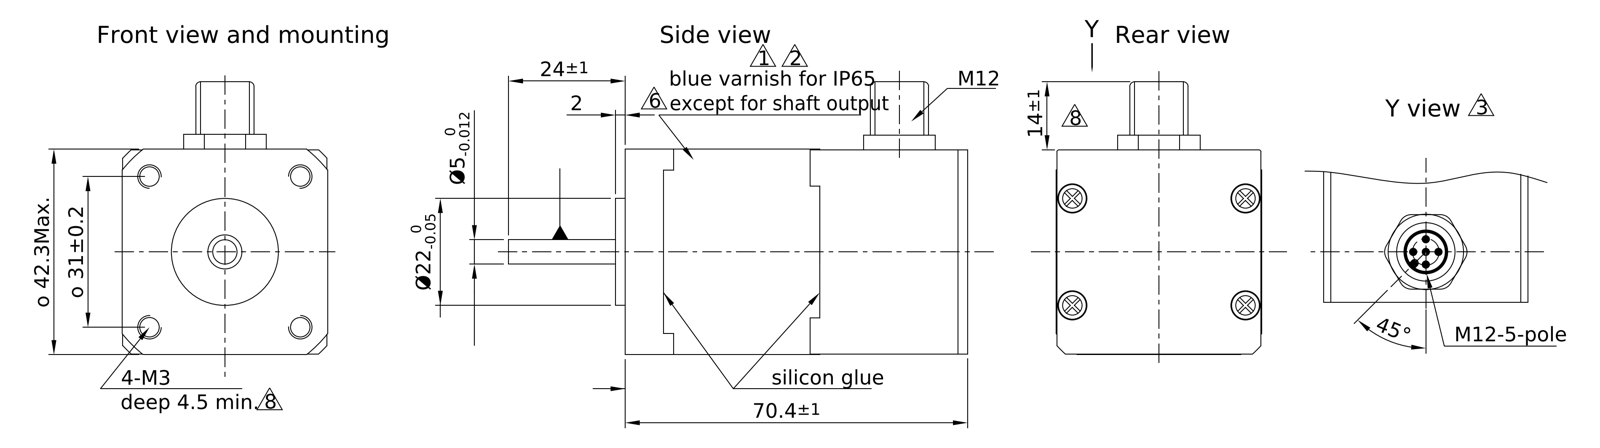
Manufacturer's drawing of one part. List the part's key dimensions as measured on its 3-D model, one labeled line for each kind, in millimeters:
Part name (STEP PRODUCT): AS4118L1804; ST4118L1804-CB1; MG-D41; MG-AK41-M12 (+2 more)
STEP written by: Autodesk Inventor 2010 (AUTOMOTIVE_DESIGN)
Units: millimetres
Bodies: 8 solids, 366 faces (139 planar, 96 cylindrical, 131 other)
Overall size (bounding box): 94.42 × 56 × 42
Volume: 87 072 mm³ · Surface area: 29 824 mm²
Round holes (diameter × count): ⌀2.9 ×4, ⌀7 ×1, ⌀8.3 ×1, ⌀9.2 ×1, ⌀10 ×1, ⌀12 ×1, ⌀16 ×1, ⌀32 ×1
Round bosses / shafts (diameter × count): ⌀1 ×5, ⌀4.7 ×4, ⌀2.5 ×4, ⌀2.22 ×4, ⌀22 ×1, ⌀21.95 ×1, ⌀12 ×1, ⌀10.5 ×1
Partial cylindrical surfaces — rounded edges, fillets, slot ends (radius × count): R3 ×17, R0.4 ×8, R5 ×6, R1.8 ×4, R1.5 ×2, R0.5 ×1, R24.8 ×1, R25 ×1
Main face-to-face distances: 41.8, 42, 2, 28.4, 30.4, 41.6, 70.4, 2.2, 39.8, 39.6
Hole centre spacings: 20.92, 22, 35.6, 41.85
